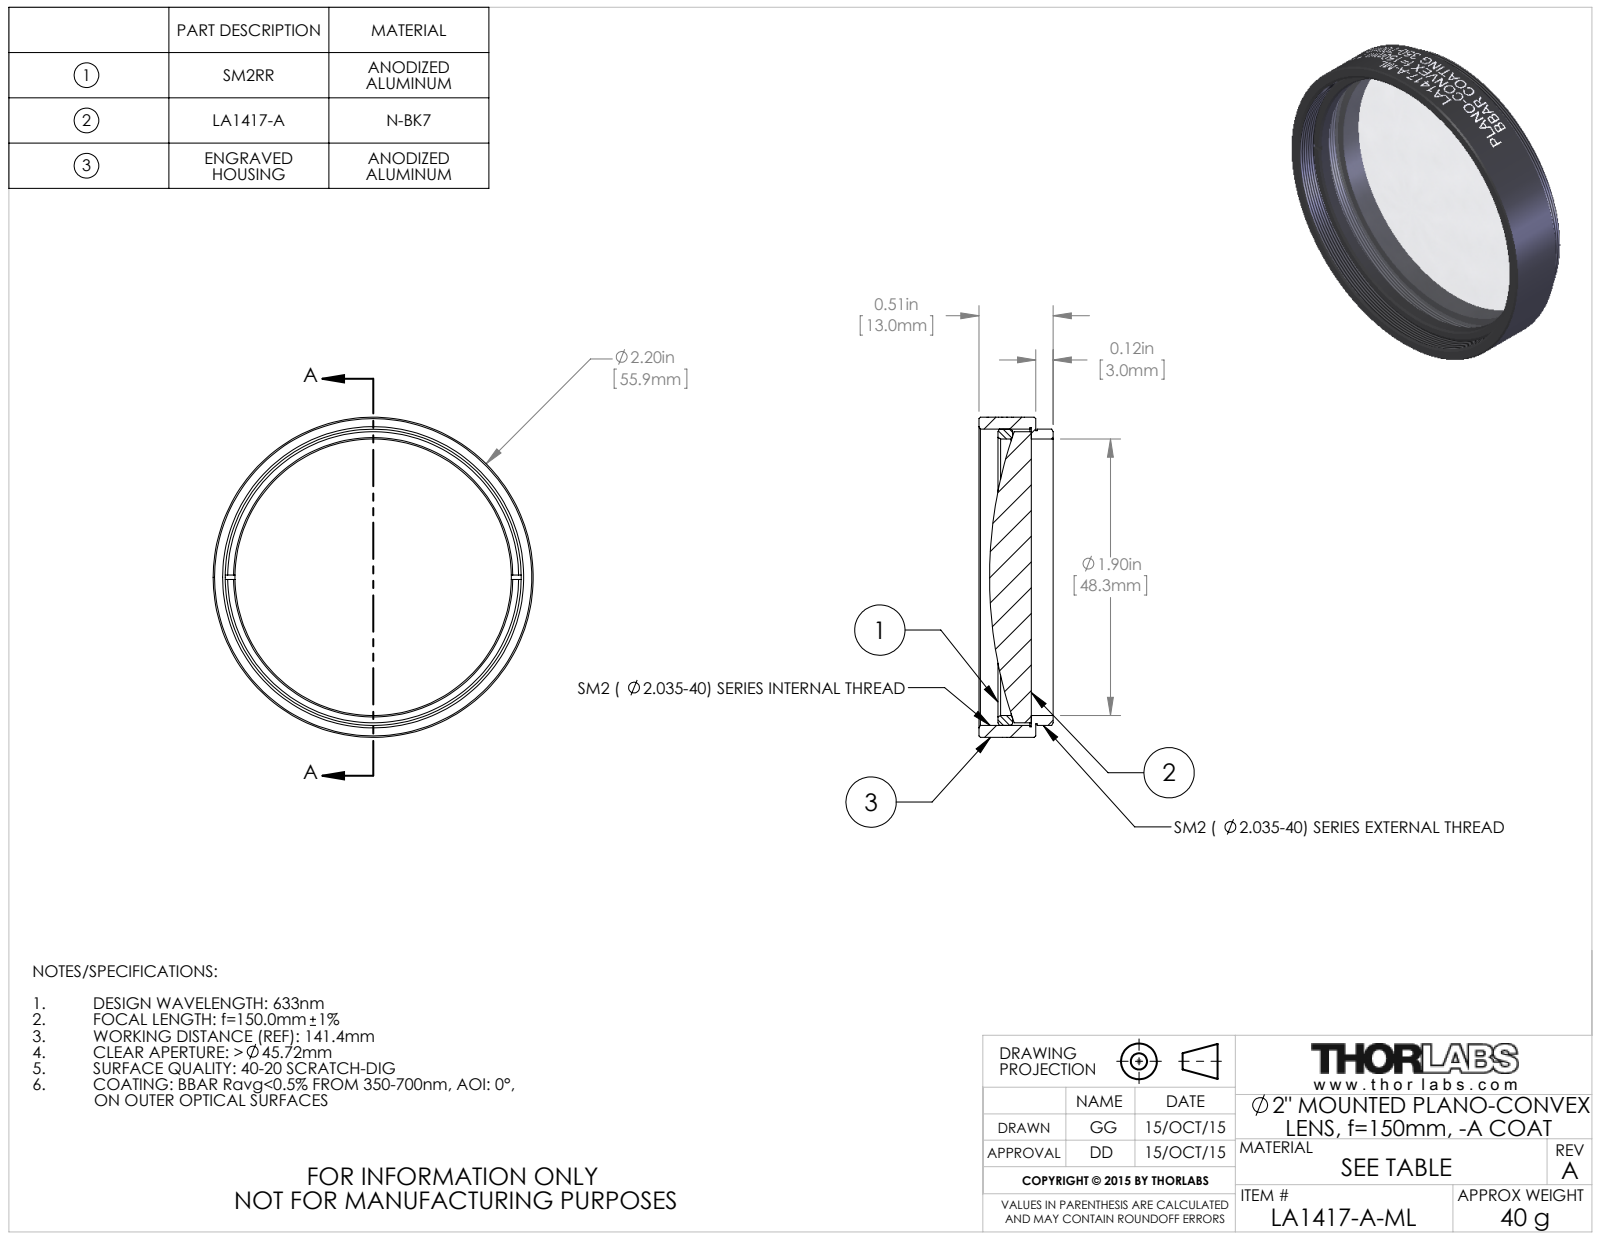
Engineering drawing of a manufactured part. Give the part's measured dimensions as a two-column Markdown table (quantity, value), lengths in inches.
| quantity | value |
| --- | --- |
| part name | TTN039585-E0W |
| STEP written by | SolidWorks 2014 (CONFIG_CONTROL_DESIGN) |
| units | inches |
| bodies | 3 solids, 141 faces (16 planar, 105 cylindrical, 20 other) |
| overall size | 2.2 × 2.2 × 0.51 |
| volume | 0.952 in³ |
| surface area | 17.68 in² |
| round holes (diameter × count) | 1.9 × 1, 2.055 × 1 |
| round bosses / shafts (diameter × count) | 2.2 × 1, 2.035 × 1, 2.015 × 1, 2 × 1 |
| main face-to-face distances | 0.03, 0.39, 0.36, 0.12, 0.15, 0.51, 0.279, 0.159, 0.129, 0.231 |
